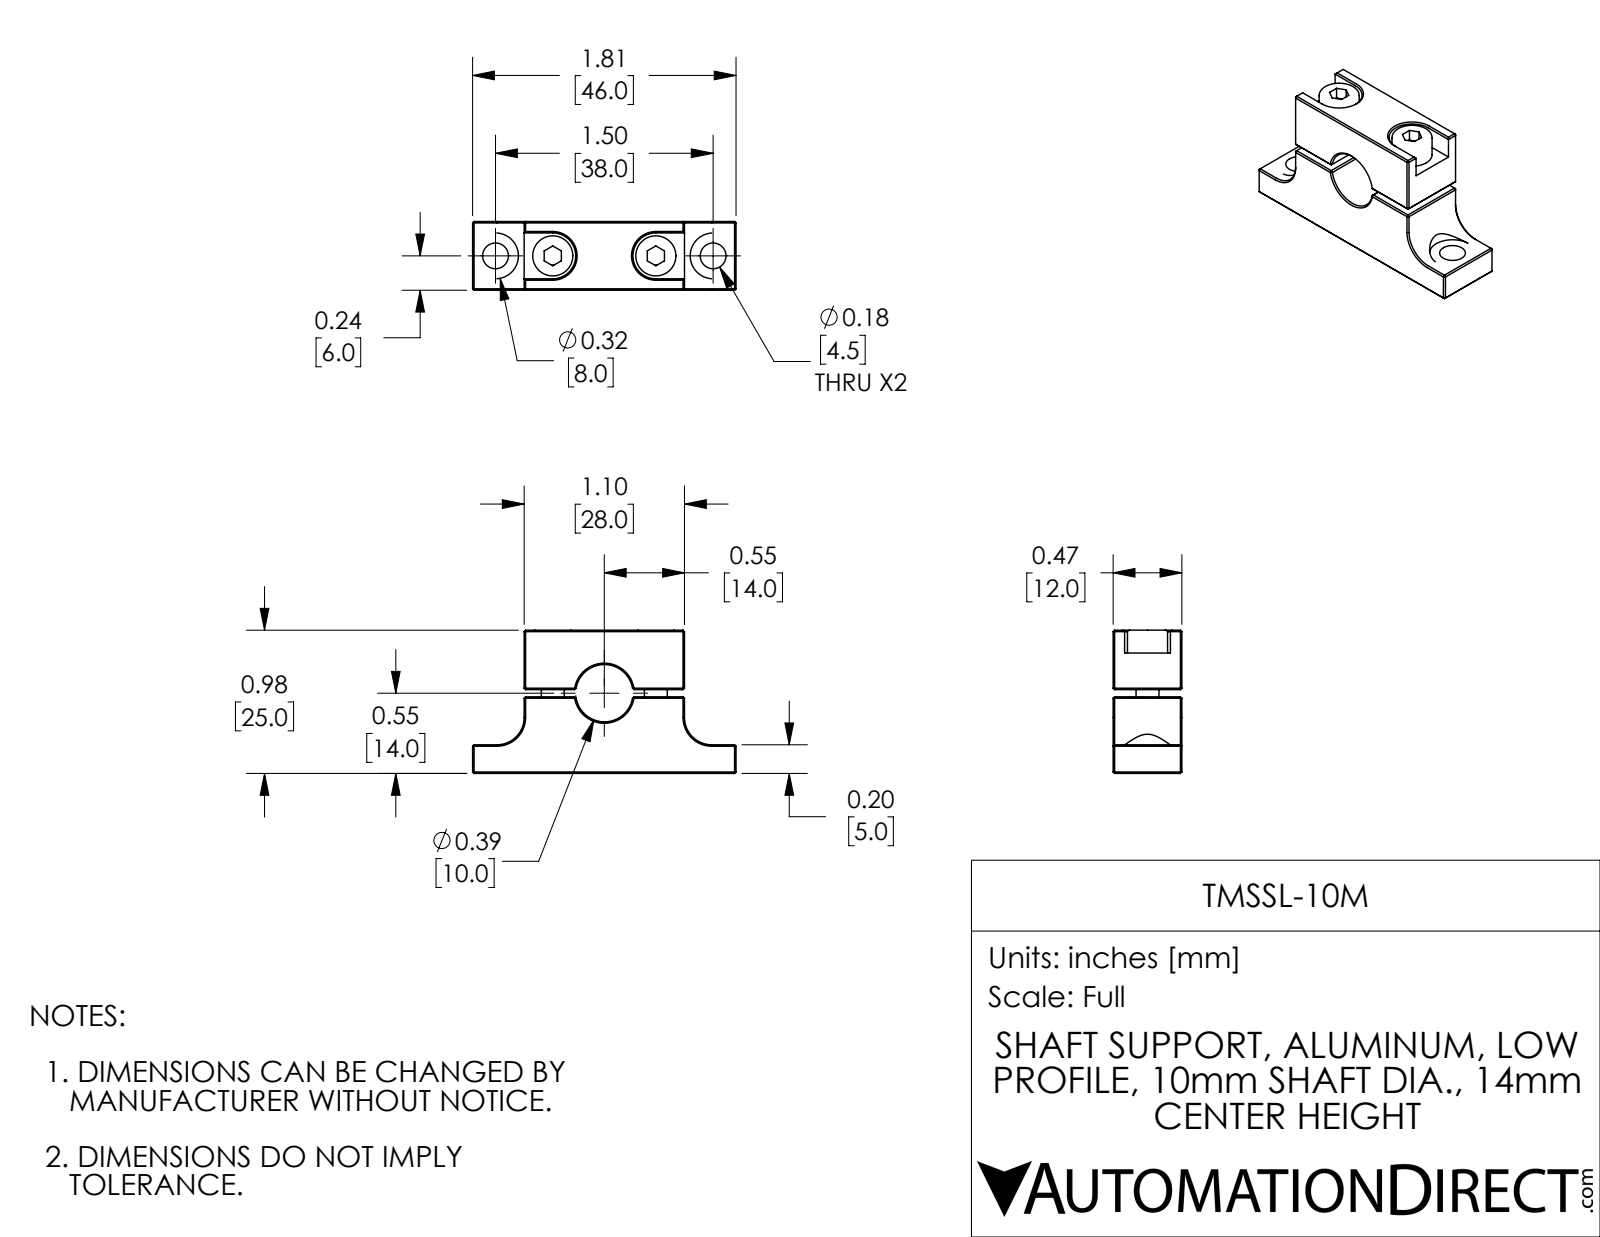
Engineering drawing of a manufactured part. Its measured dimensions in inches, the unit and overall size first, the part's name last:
Units: inches
Overall size (bounding box): 1.811 × 0.985 × 0.472
Round holes (diameter × count): ⌀0.177 ×4, ⌀0.128 ×2, ⌀0.094 ×1, ⌀0.394 ×1
Round bosses / shafts (diameter × count): ⌀0.276 ×2, ⌀0.157 ×2
Partial cylindrical surfaces — rounded edges, fillets, slot ends (radius × count): R0.158 ×4, R0.187 ×2
Main face-to-face distances: 0.472, 0.984, 0.049, 0.827, 0.157, 0.458, 0.409, 1.102, 0.354, 0.197
Hole centre spacings: 0.354, 0.394, 0.748, 1.102, 0.709, 1.496
Volume: 0.476 in³ · Surface area: 7.678 in²
Bodies: 4 solids, 179 faces (118 planar, 32 cylindrical, 29 other)
Part name (STEP PRODUCT): TMSSL-10M
STEP written by: SolidWorks 2017 (AUTOMOTIVE_DESIGN)
